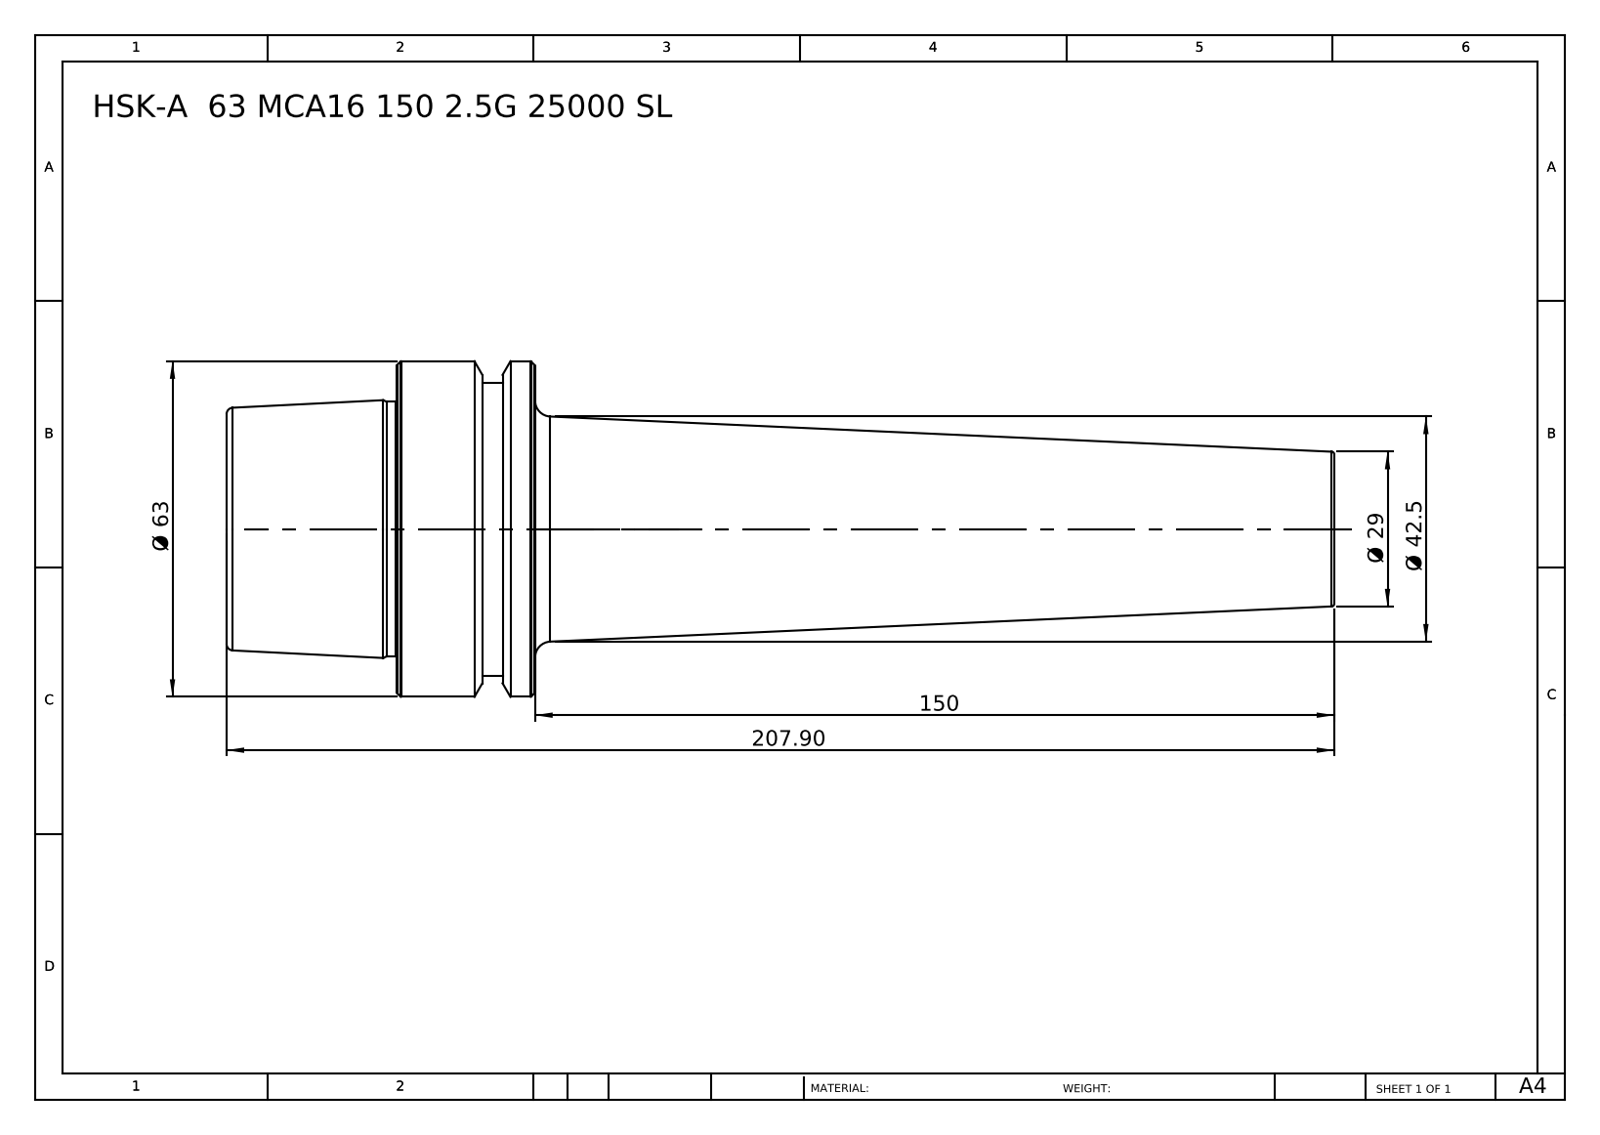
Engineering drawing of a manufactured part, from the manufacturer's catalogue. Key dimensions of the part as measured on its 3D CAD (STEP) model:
Part name (STEP PRODUCT): HSK-A 63 MCA16 150 2.5G 25000 SL
STEP written by: SolidWorks 2014 (CONFIG_CONTROL_DESIGN)
Units: millimetres
Bodies: 1 solid, 46 faces (6 planar, 8 cylindrical, 32 other)
Overall size (bounding box): 207.9 × 63 × 63
Volume: 285 188 mm³ · Surface area: 32 586 mm²
Round bosses / shafts (diameter × count): ⌀63 ×1, ⌀55 ×1, ⌀47.78 ×1
Main face-to-face distances: 57.9, 26, 31.9, 150, 176, 207.9, 156.1, 6.1, 19.9, 51.8
